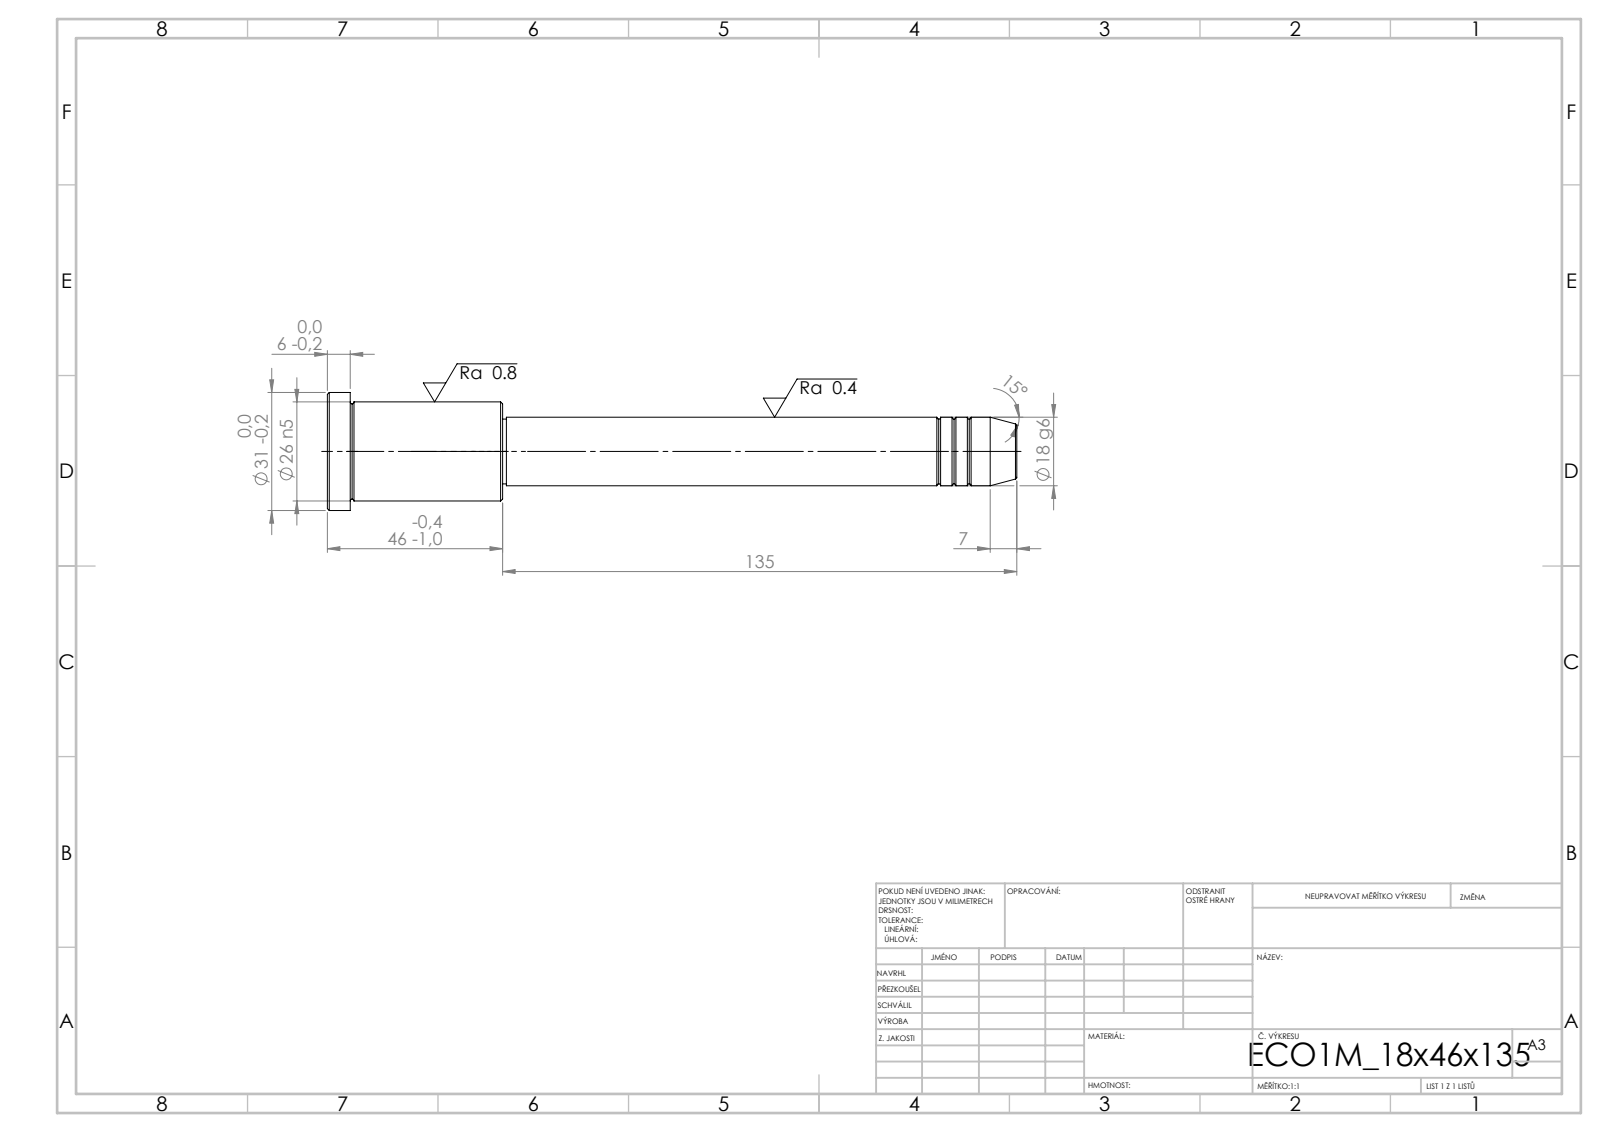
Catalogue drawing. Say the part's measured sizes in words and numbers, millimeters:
Its 3-D file was written by "SolidWorks 2019 (CONFIG_CONTROL_DESIGN)". It is 1 solid with 43 faces: 5 planar, 14 cylindrical and 24 other. Overall it measures 181 by 31 by 31 millimeters. Its volume is 59 626 cubic millimeters and its surface area 12 996 square millimeters. Round bosses or shafts: 1 of diameter 31, 1 of diameter 26, 1 of diameter 18, 1 of diameter 17. The main face-to-face distances are 46, 40, 6, 135, 175, 181, 134, 1, 41, 47.
